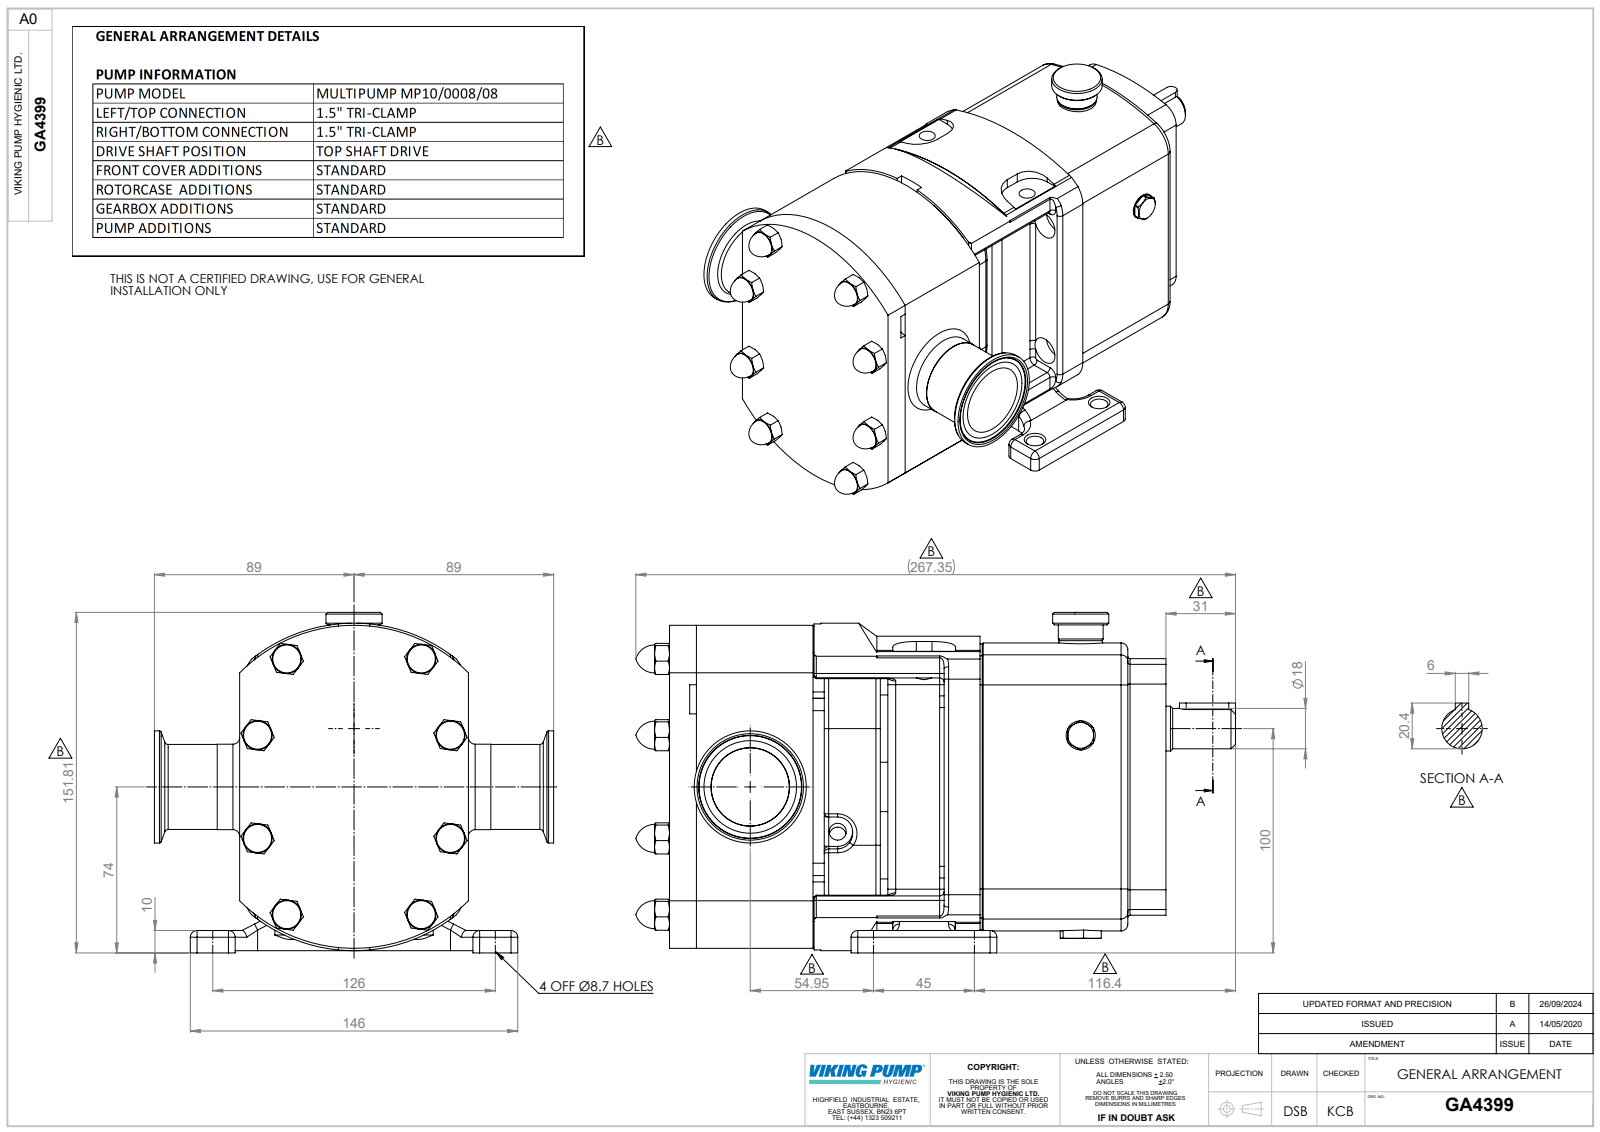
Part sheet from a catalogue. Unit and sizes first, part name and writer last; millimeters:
Units: millimetres
Overall size (bounding box): 267.35 × 178 × 151.81
Round holes (diameter × count): ⌀8.7 ×4, ⌀14 ×4, ⌀7.63 ×2, ⌀8 ×2, ⌀22.53 ×1, ⌀34.85 ×1, ⌀35 ×1
Round bosses / shafts (diameter × count): ⌀30 ×2, ⌀50 ×1, ⌀38.1 ×1, ⌀37.9 ×1, ⌀25.02 ×1, ⌀19.99 ×1, ⌀19.98 ×1, ⌀19.5 ×1
Partial cylindrical surfaces — rounded edges, fillets, slot ends (radius × count): R2 ×30, R3 ×26, R13.5 ×12, R10.5 ×8, R3.5 ×6, R5.5 ×4, R6 ×4, R9 ×4
Main face-to-face distances: 5, 221.35, 124, 102, 96.99, 5.01, 91.99, 97, 97.35, 21
Hole centre spacings: 35.92, 100.55, 45, 76, 77.02, 108.2, 126, 133.79
Volume: 2 464 000 mm³ · Surface area: 192 068 mm²
Bodies: 3 solids, 764 faces (254 planar, 218 cylindrical, 292 other)
Part name (STEP PRODUCT): Copy of Z94-5121-22 - 1.5 INCH^GA4399; Copy of CP10-0008-08 H T^GA4399; GA4399
STEP written by: SolidWorks 2023 (AUTOMOTIVE_DESIGN)
